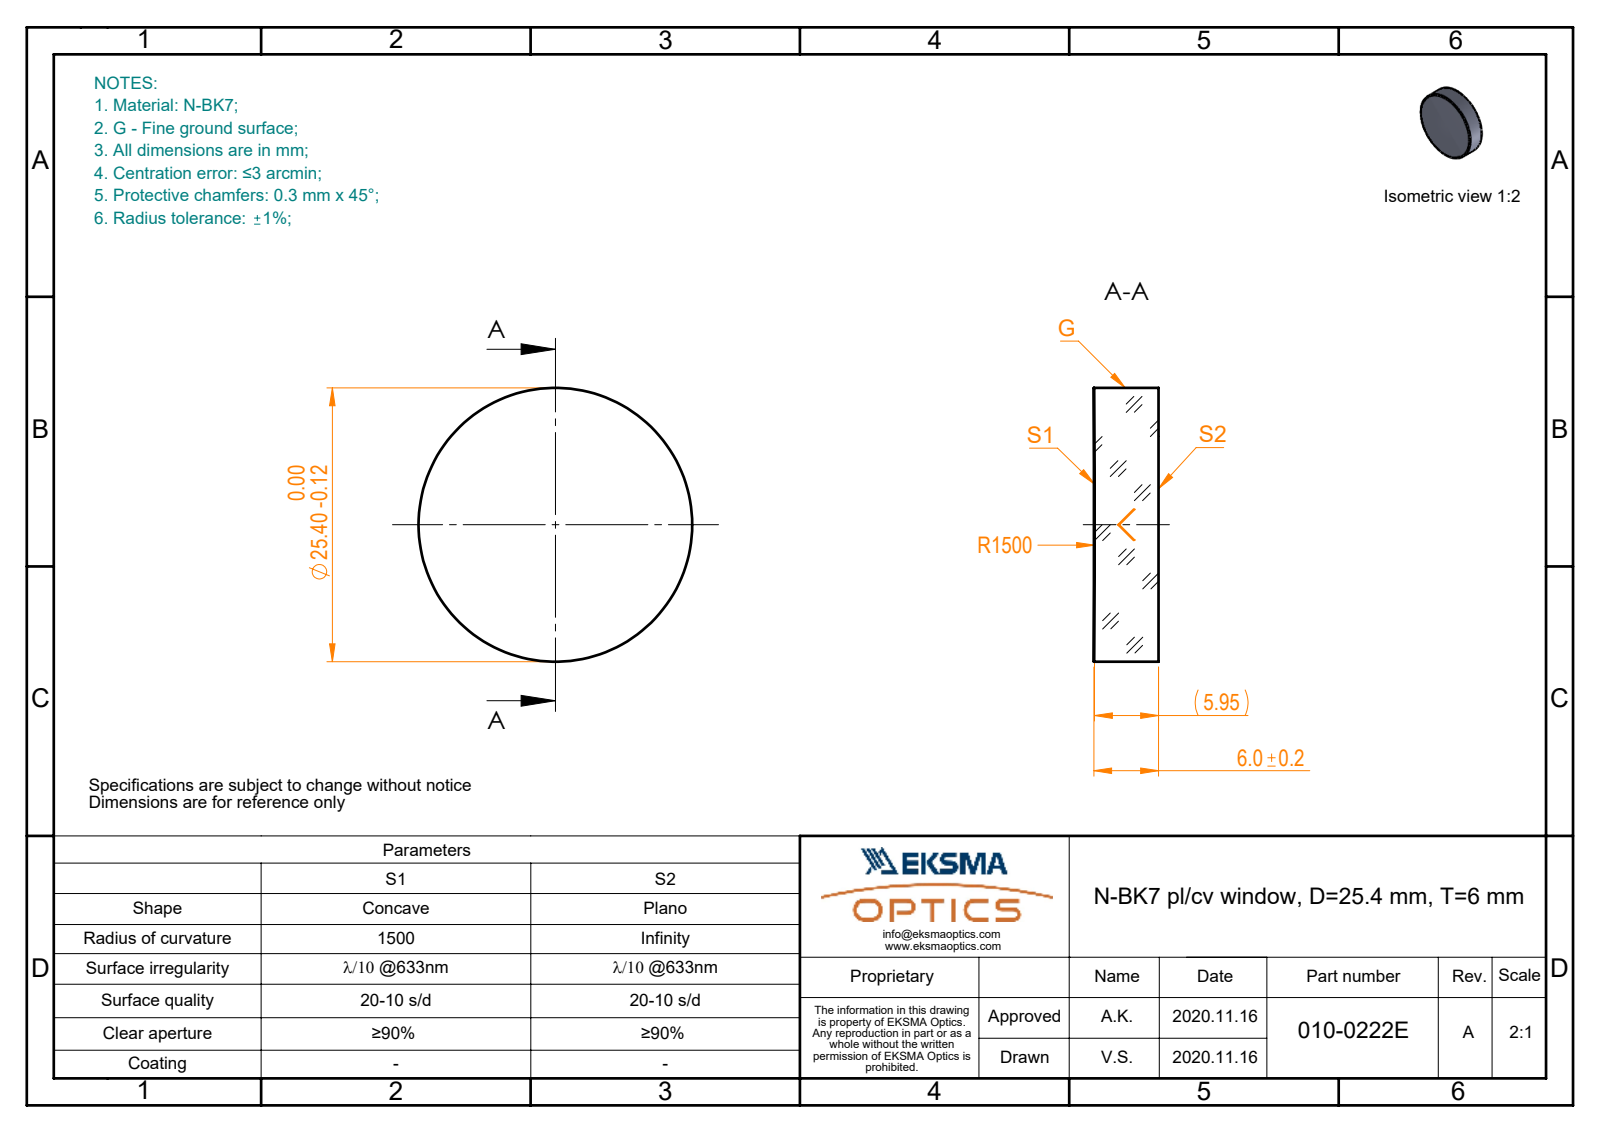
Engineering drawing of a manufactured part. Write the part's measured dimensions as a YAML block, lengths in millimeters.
part_name: "010-0222E_N-BK7_PCV_window"
step_written_by: "SolidWorks 2019 (CONFIG_CONTROL_DESIGN)"
units: millimeters
bodies: {solids: 1, faces: 5, planar: 1, cylindrical: 2, other: 2}
overall_size: [25.4, 25.4, 6]
volume: 3027
surface_area: 1492
round_bosses_or_shafts:
  - {diameter: 25.4, count: 1}
